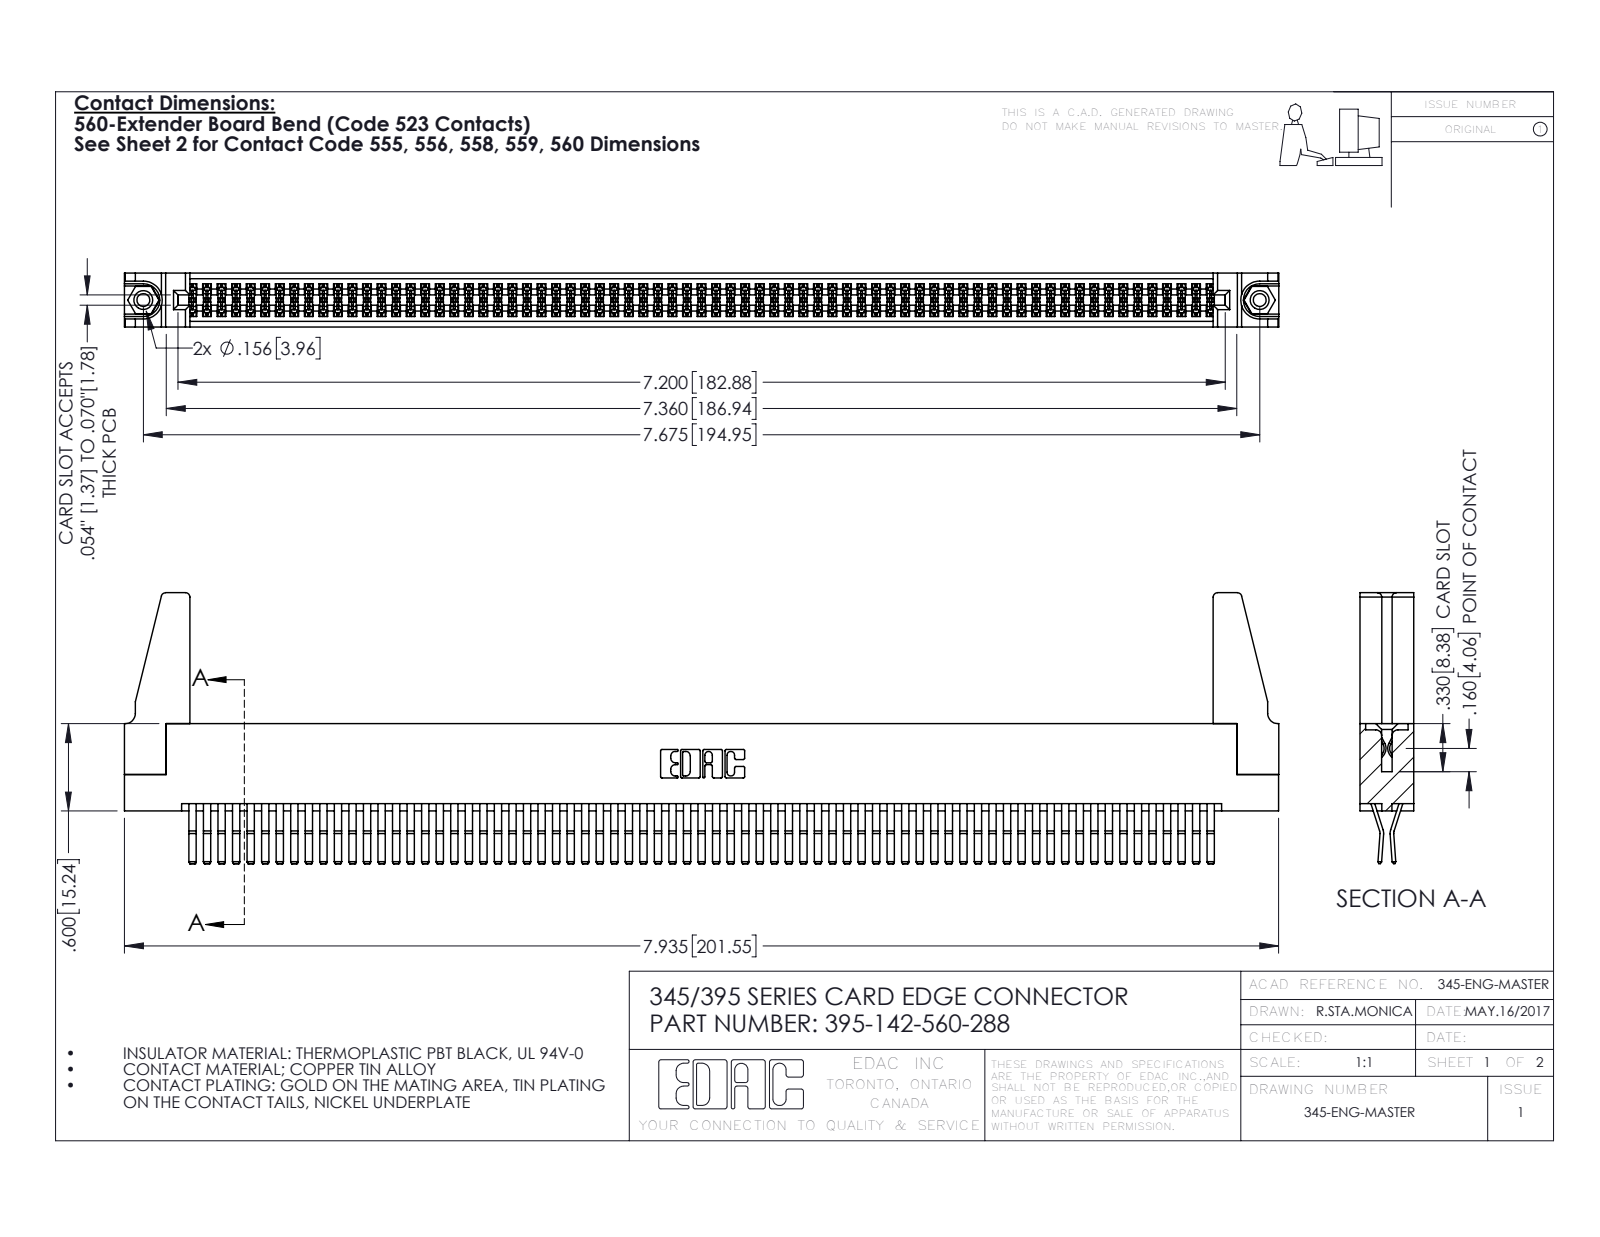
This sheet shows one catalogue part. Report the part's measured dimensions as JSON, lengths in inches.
{"part_name": "345-220-078_345-220-088; 345-292-001_560 Tail; 345 Part_Flush Mounting Lugs - 0.156 Dia-TH; 395-142-560-288 (+1 more)", "step_written_by": "SolidWorks 2016 (CONFIG_CONTROL_DESIGN)", "units": "inches", "bodies": {"solids": 147, "faces": 7634, "planar": 4838, "cylindrical": 2780, "other": 16}, "overall_size": [7.936, 1.862, 0.37], "volume_in3": 1.467, "surface_area_in2": 57.03, "round_holes": [[0.089, 2], [0.125, 2], [0.156, 2], [0.064, 1]], "round_bosses_or_shafts": [[0.155, 2]], "partial_cylinders_radius": [[0.006, 213], [0.01, 22], [0.03, 8], [0.007, 6], [0.031, 6], [0.026, 3], [0.01, 2], [0.014, 2]], "face_to_face_distances": [0.072, 0.025, 0.298, 0.37, 0.2, 0.098, 0.272, 0.225, 0.175, 0.149], "hole_center_spacings": [0.27, 7.439, 7.675]}
